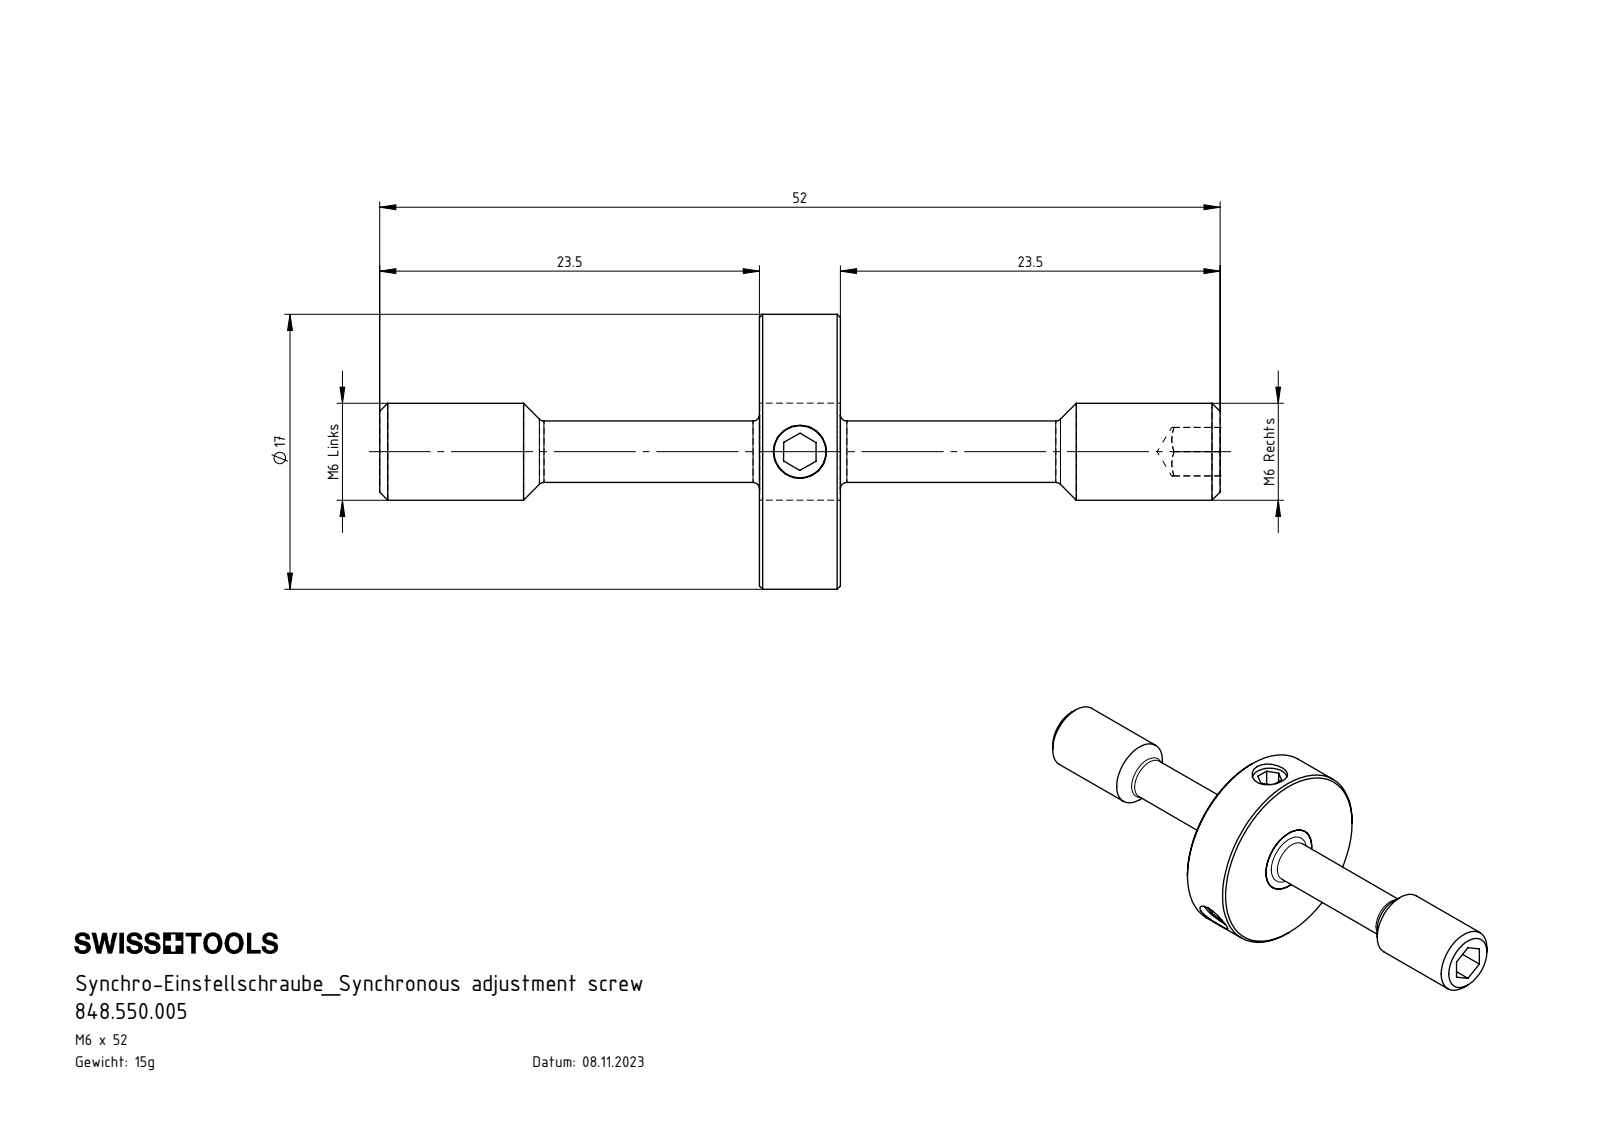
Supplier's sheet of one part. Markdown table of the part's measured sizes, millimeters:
| quantity | value |
| --- | --- |
| part name | ISO 4026 - M4 x 5; Z42-ER3.002.005_A; Z55-ER3.001.052_A; 848.550.005 |
| STEP written by | SolidWorks 2022 (AUTOMOTIVE_DESIGN) |
| units | millimeters |
| bodies | 5 solids, 99 faces (39 planar, 26 cylindrical, 34 other) |
| overall size | 52 × 17 × 17 |
| volume | 1 964 mm³ |
| surface area | 2 067 mm² |
| round holes (diameter × count) | 3.3 × 3 |
| round bosses / shafts (diameter × count) | 4 × 3, 17 × 1, 6 × 1, 3.8 × 1 |
| main face-to-face distances | 5, 23.5, 28.5, 2, 2.5, 3, 52, 25, 27, 1.5 |
